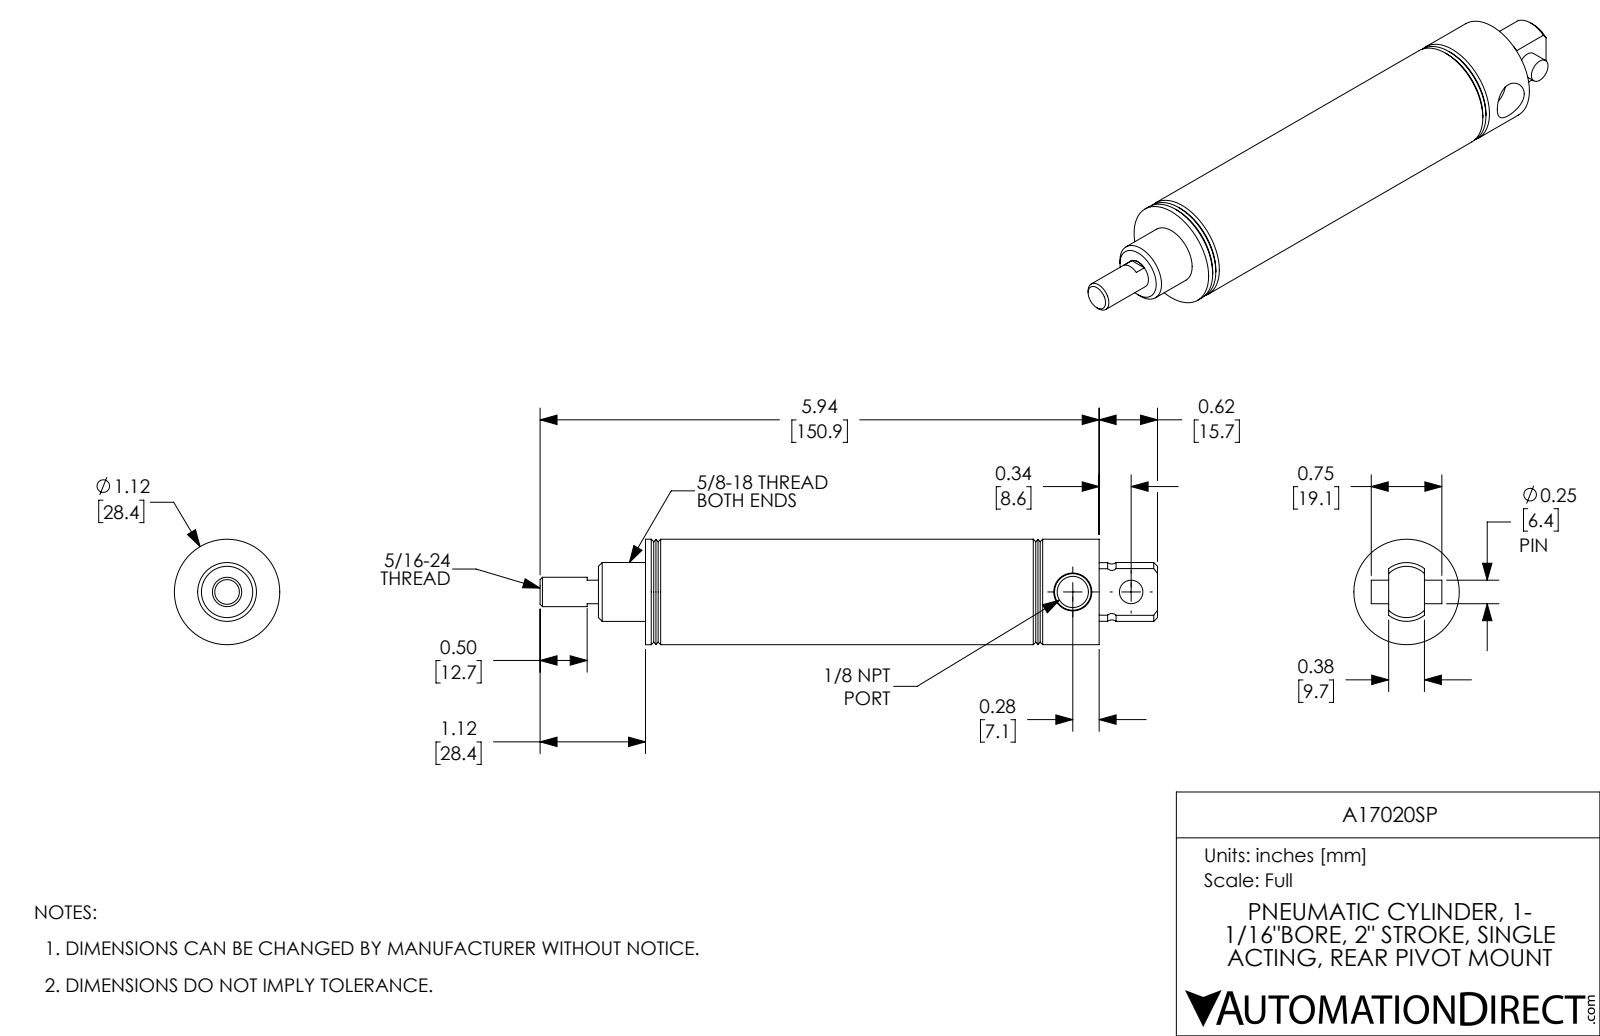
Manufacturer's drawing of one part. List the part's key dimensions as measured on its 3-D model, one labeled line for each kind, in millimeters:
Part name (STEP PRODUCT): A17020SP-Rod; A17020SP-MainBody; A17020SP-PIN; A17020SP
STEP written by: SolidWorks 2017 (AUTOMOTIVE_DESIGN)
Units: millimetres
Bodies: 3 solids, 76 faces (20 planar, 26 cylindrical, 30 other)
Overall size (bounding box): 166.6 × 28.4 × 28.4
Volume: 56 030 mm³ · Surface area: 27 010 mm²
Round holes (diameter × count): ⌀6.4 ×1, ⌀7.9 ×1, ⌀8.4 ×1, ⌀27 ×1
Round bosses / shafts (diameter × count): ⌀28.4 ×1, ⌀15.9 ×1
Partial cylindrical surfaces — rounded edges, fillets, slot ends (radius × count): R7.9 ×1
Main face-to-face distances: 12.7, 93, 63.5, 50.8, 29.5, 42.2, 93, 122.4, 80.3, 29.5
Hole centre spacings: 15.7
